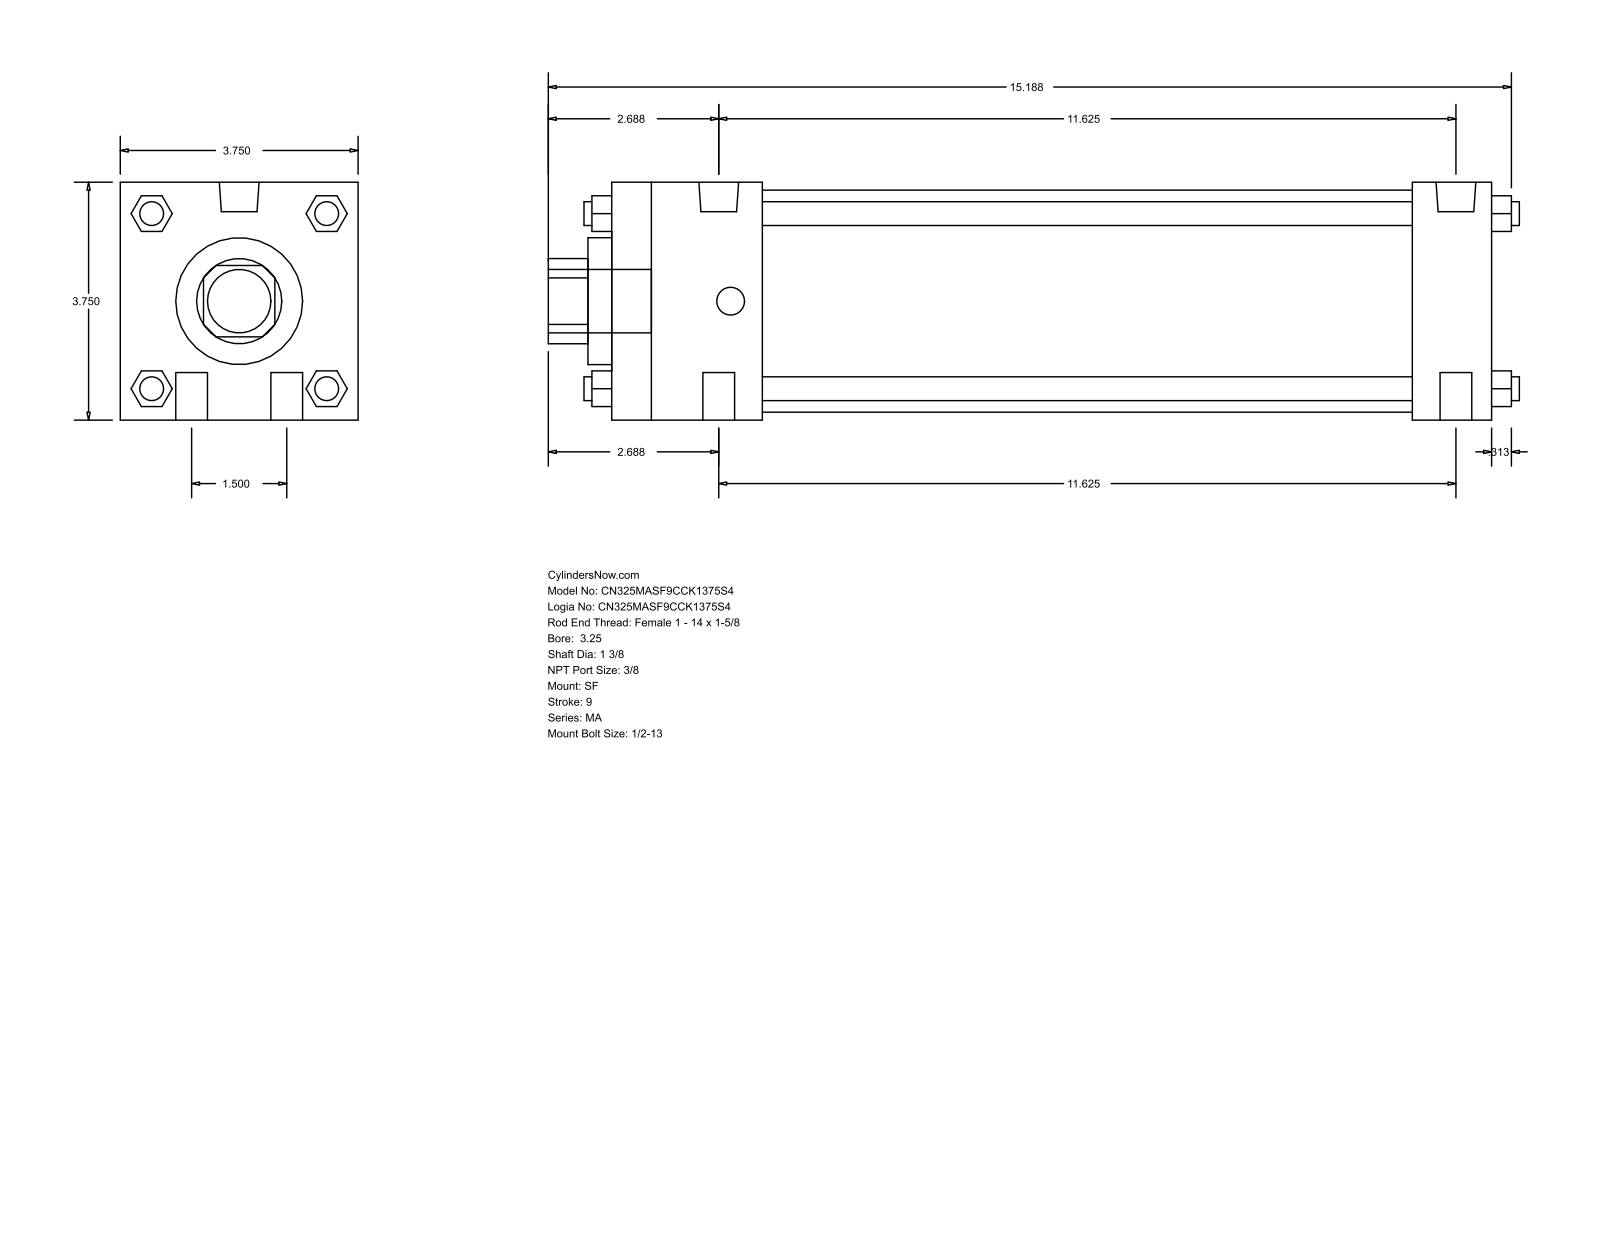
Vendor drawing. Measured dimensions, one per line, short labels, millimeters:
name: MA_SF__0325_1.375
written by: GSSL Pune (CONFIG_CONTROL_DESIGN)
unit: mm
bodies: 0 solids, 124 faces (94 planar, 30 cylindrical, 0 other)
size: 388.94 × 95.25 × 95.25
holes: 1× ⌀34.92, 1× ⌀50.8, 1× ⌀88.9
bosses: 4× ⌀12.7, 4× ⌀9.53, 2× ⌀15.93, 2× ⌀11.11, 1× ⌀25.4
rounds: 1× R17.06
face distances: 95.24, 352.42, 320.67, 31.75, 60.32, 260.35, 292.1, 9.52, 69.84, 330.19
